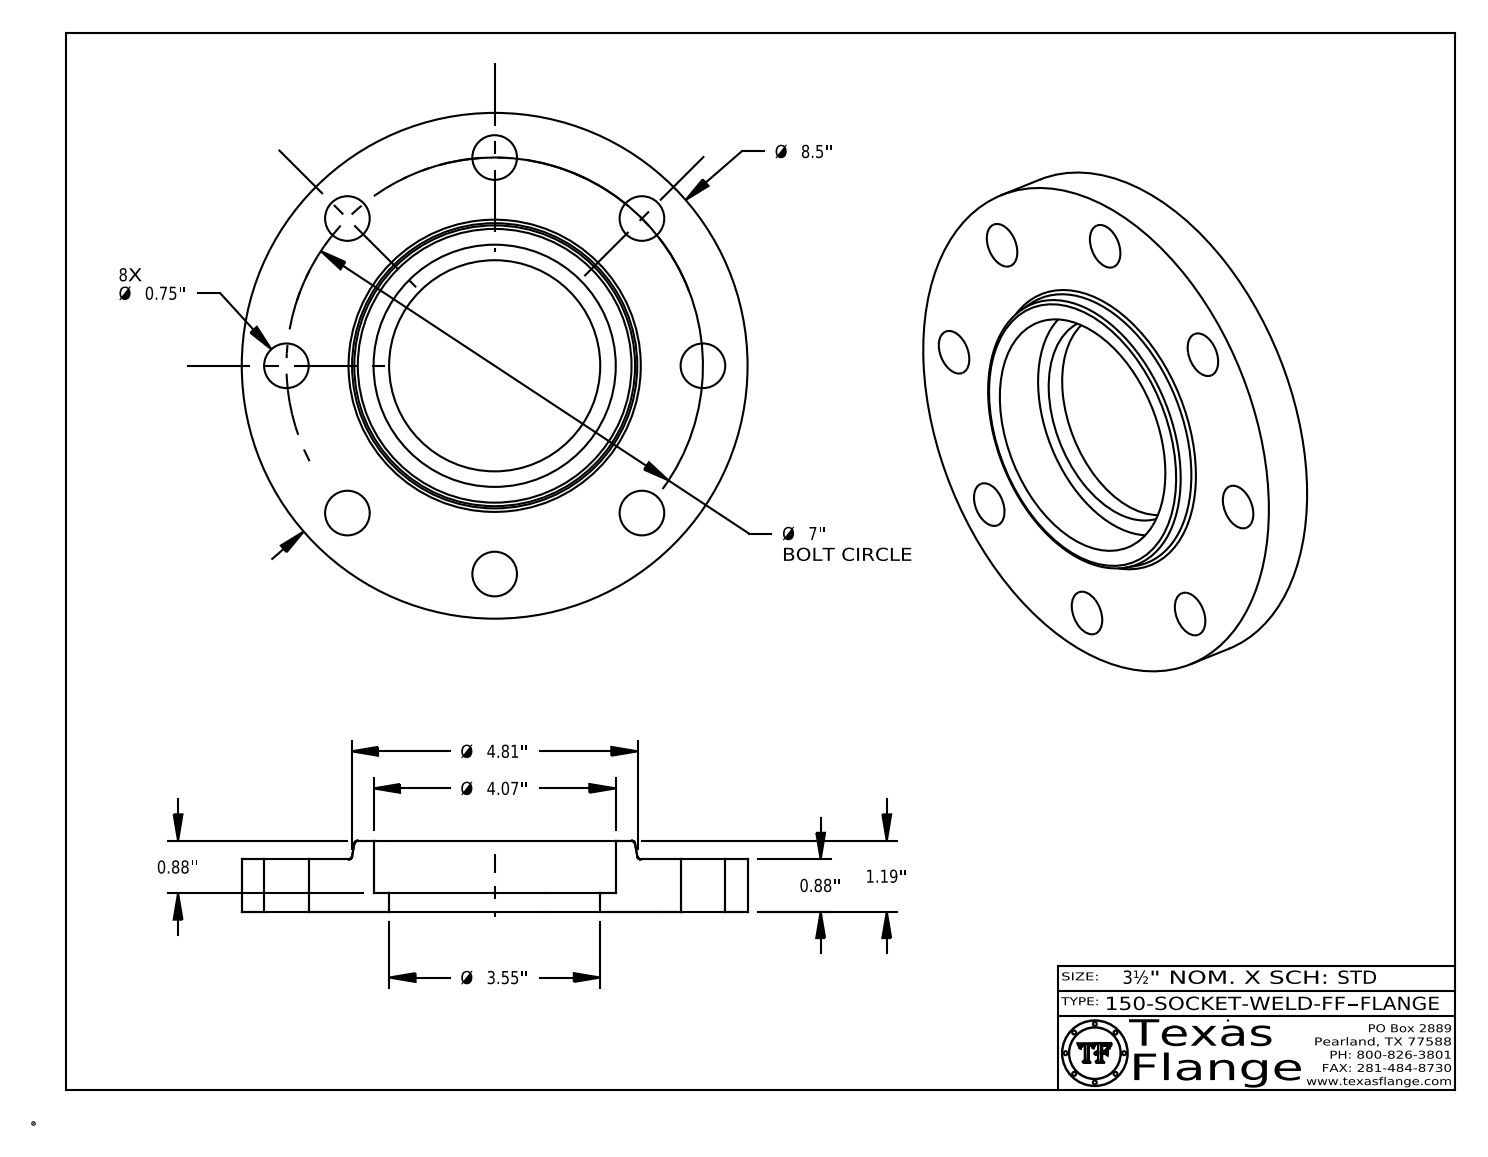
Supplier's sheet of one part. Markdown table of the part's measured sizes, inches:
| quantity | value |
| --- | --- |
| part name | 150-SOCKET-WELD-FF |
| STEP written by | CATIA V5 STEP AP214 (AUTOMOTIVE_DESIGN) |
| units | inches |
| bodies | 1 solid, 418 faces (370 planar, 42 cylindrical, 6 other) |
| overall size | 8.5 × 8.5 × 1.19 |
| volume | 37.82 in³ |
| surface area | 144.9 in² |
| round holes (diameter × count) | 0.75 × 8, 0.495 × 1, 3.548 × 1, 4.07 × 1 |
| round bosses / shafts (diameter × count) | 0.03 × 8, 8.5 × 1, 0.39 × 1 |
| main face-to-face distances | 0.88, 1.19, 0.31, 0.31, 0.57, 0.88, 0.865, 0.555, 0.015, 0.325 |
| hole center spacings | 3.5, 2.679, 4.95, 6.467, 1.366, 3.889, 5.82, 6.865 |
